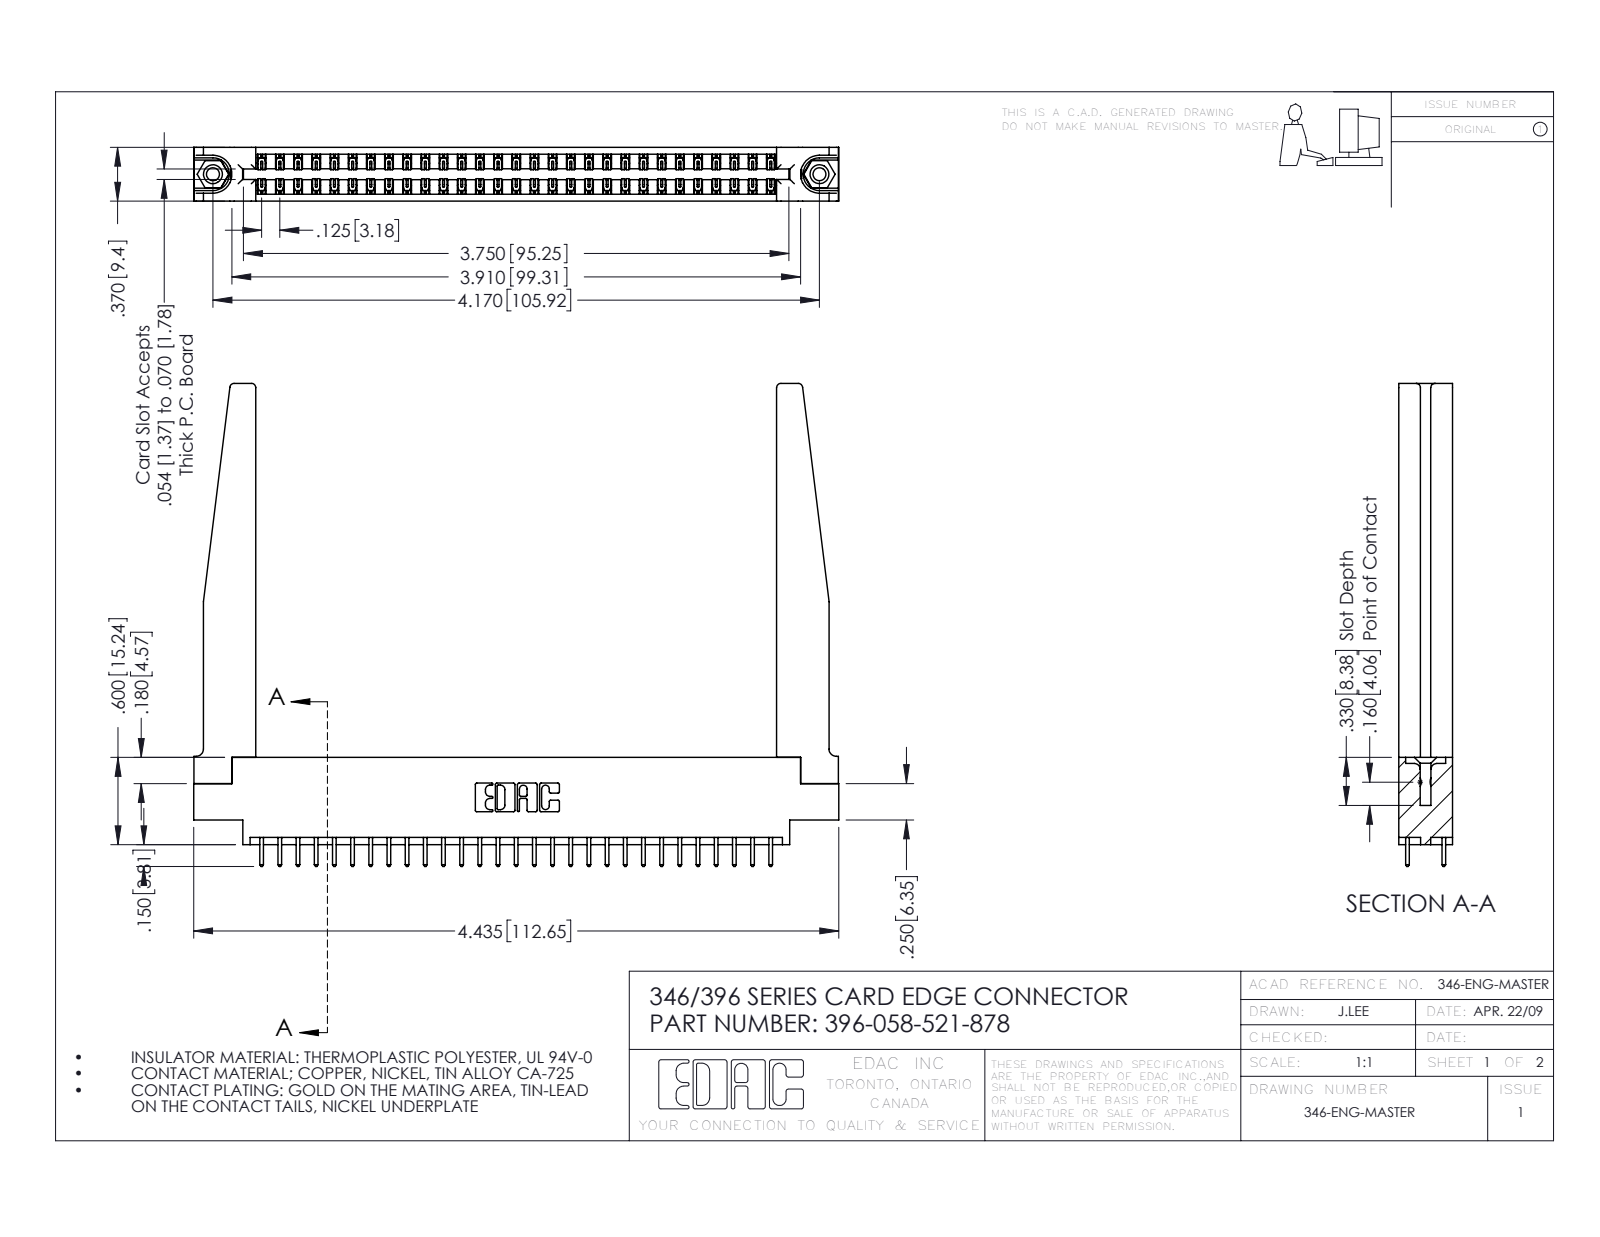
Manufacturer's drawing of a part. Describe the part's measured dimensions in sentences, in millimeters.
The part is named "346-220-078_345-220-078; 346 Part_0.170 Offset - 0.156 Dia-TH; 345-292-001_345-293-121; 396-058-521-878 (+1 more)". Its 3-D file was written by "SolidWorks 2016 (CONFIG_CONTROL_DESIGN)". It is 63 solids with 3376 faces: 2252 planar, 1072 cylindrical and 52 other. Overall it measures 112.6 by 84.3 by 9.4 millimeters. Its volume is 17 620 cubic millimeters and its surface area 21 070 square millimeters. Round holes: 2 of diameter 2.3, 2 of diameter 3.2, 2 of diameter 4, 1 of diameter 1.6. Round bosses or shafts: 2 of diameter 3.9. Partial cylindrical surfaces (rounded edges, fillets, slot ends): 87 of radius 0.2, 58 of radius 0.3, 22 of radius 0.3, 8 of radius 0.8, 6 of radius 0.2, 6 of radius 0.8, 3 of radius 0.7, 2 of radius 0.4. The main face-to-face distances are 9.4, 1.2, 8.2, 1.8, 3.8, 3.8, 6.4, 7.6, 0.6, 7. The hole center spacings are 6.2, 100.6, 105.9.
